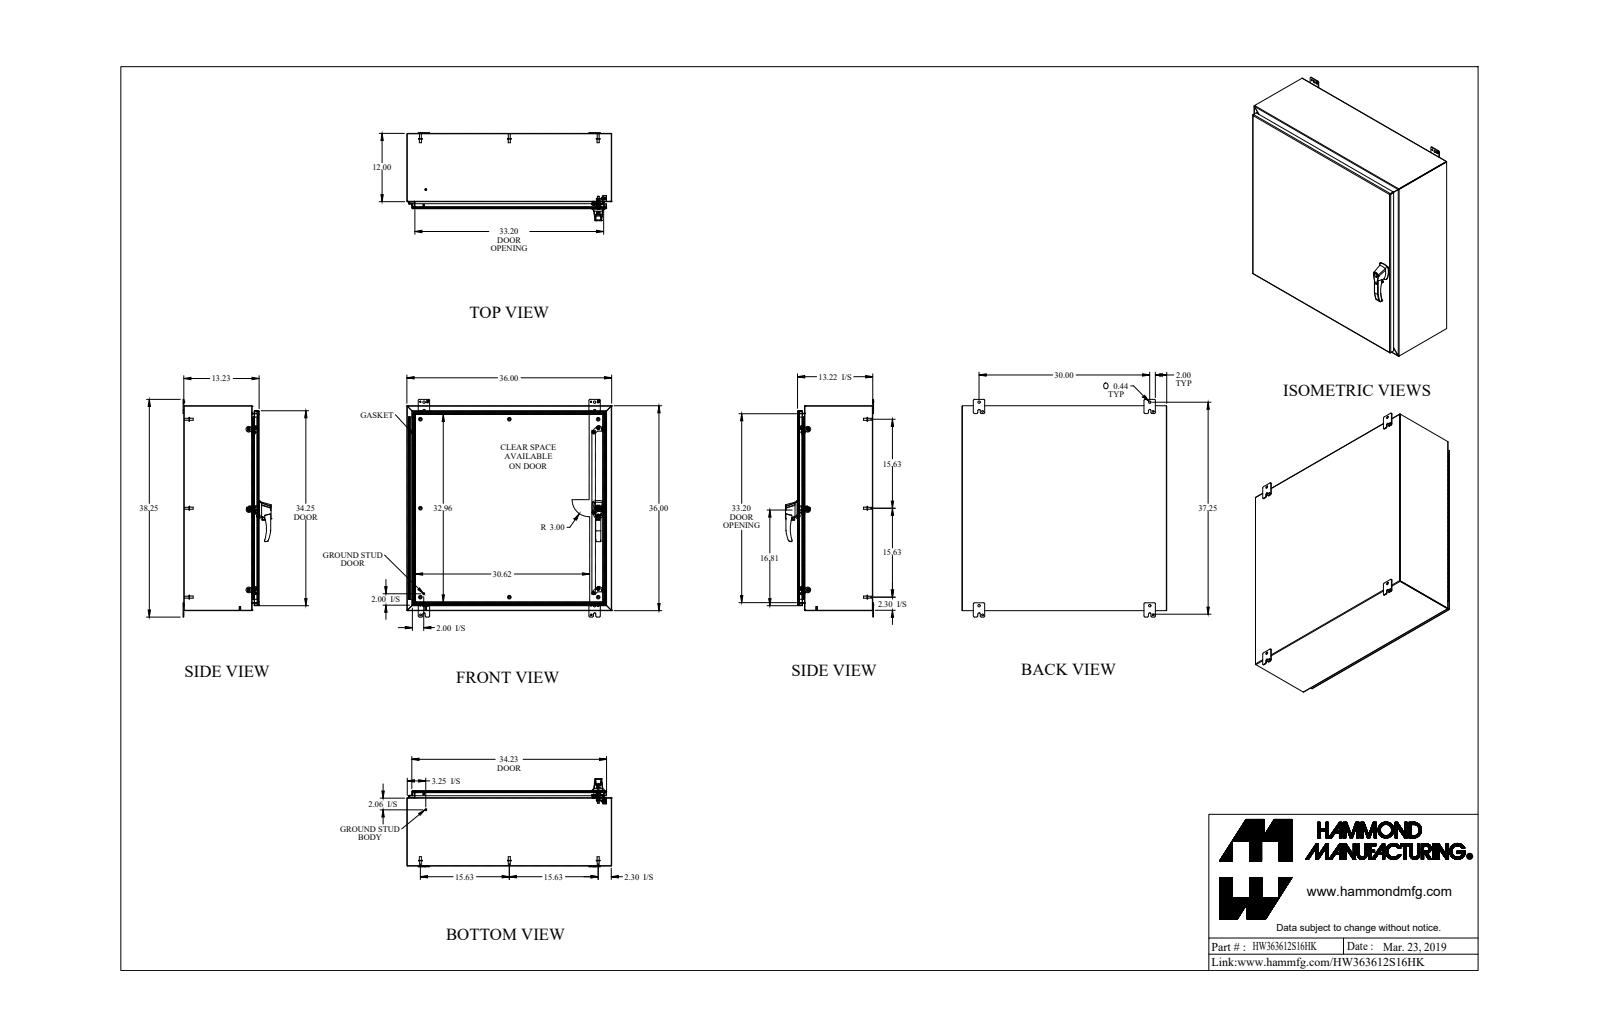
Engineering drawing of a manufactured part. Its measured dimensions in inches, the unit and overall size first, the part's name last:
Units: inches
Overall size (bounding box): 38.25 × 36 × 15.473
Round holes (diameter × count): ⌀0.176 ×6, ⌀0.313 ×4, ⌀0.25 ×3, ⌀0.265 ×3, ⌀0.413 ×3, ⌀0.196 ×2, ⌀0.256 ×2, ⌀0.394 ×2, ⌀0.437 ×2, ⌀0.11 ×1, ⌀0.233 ×1, ⌀0.33 ×1
Round bosses / shafts (diameter × count): ⌀0.375 ×13, ⌀0.65 ×8, ⌀0.332 ×8, ⌀0.25 ×7, ⌀0.156 ×6, ⌀1 ×3, ⌀0.63 ×2, ⌀0.51 ×2
Partial cylindrical surfaces — rounded edges, fillets, slot ends (radius × count): R0.25 ×27, R0.188 ×24, R0.036 ×14, R0.108 ×14, R0.06 ×12, R0.125 ×9, R0.045 ×8, R0.218 ×8
Main face-to-face distances: 0.072, 35.928, 13.138, 13.066, 0.095, 13.233, 13.161, 35.856, 36, 11.928
Hole centre spacings: 14.118, 14.119, 28.237, 1.11, 1.111, 14.119, 30, 1.004
Volume: 404.8 in³ · Surface area: 10 011 in²
Bodies: 47 solids, 1532 faces (710 planar, 654 cylindrical, 168 other)
Part name (STEP PRODUCT): HW363612S16HK
STEP written by: SolidWorks 2018 (AUTOMOTIVE_DESIGN)
